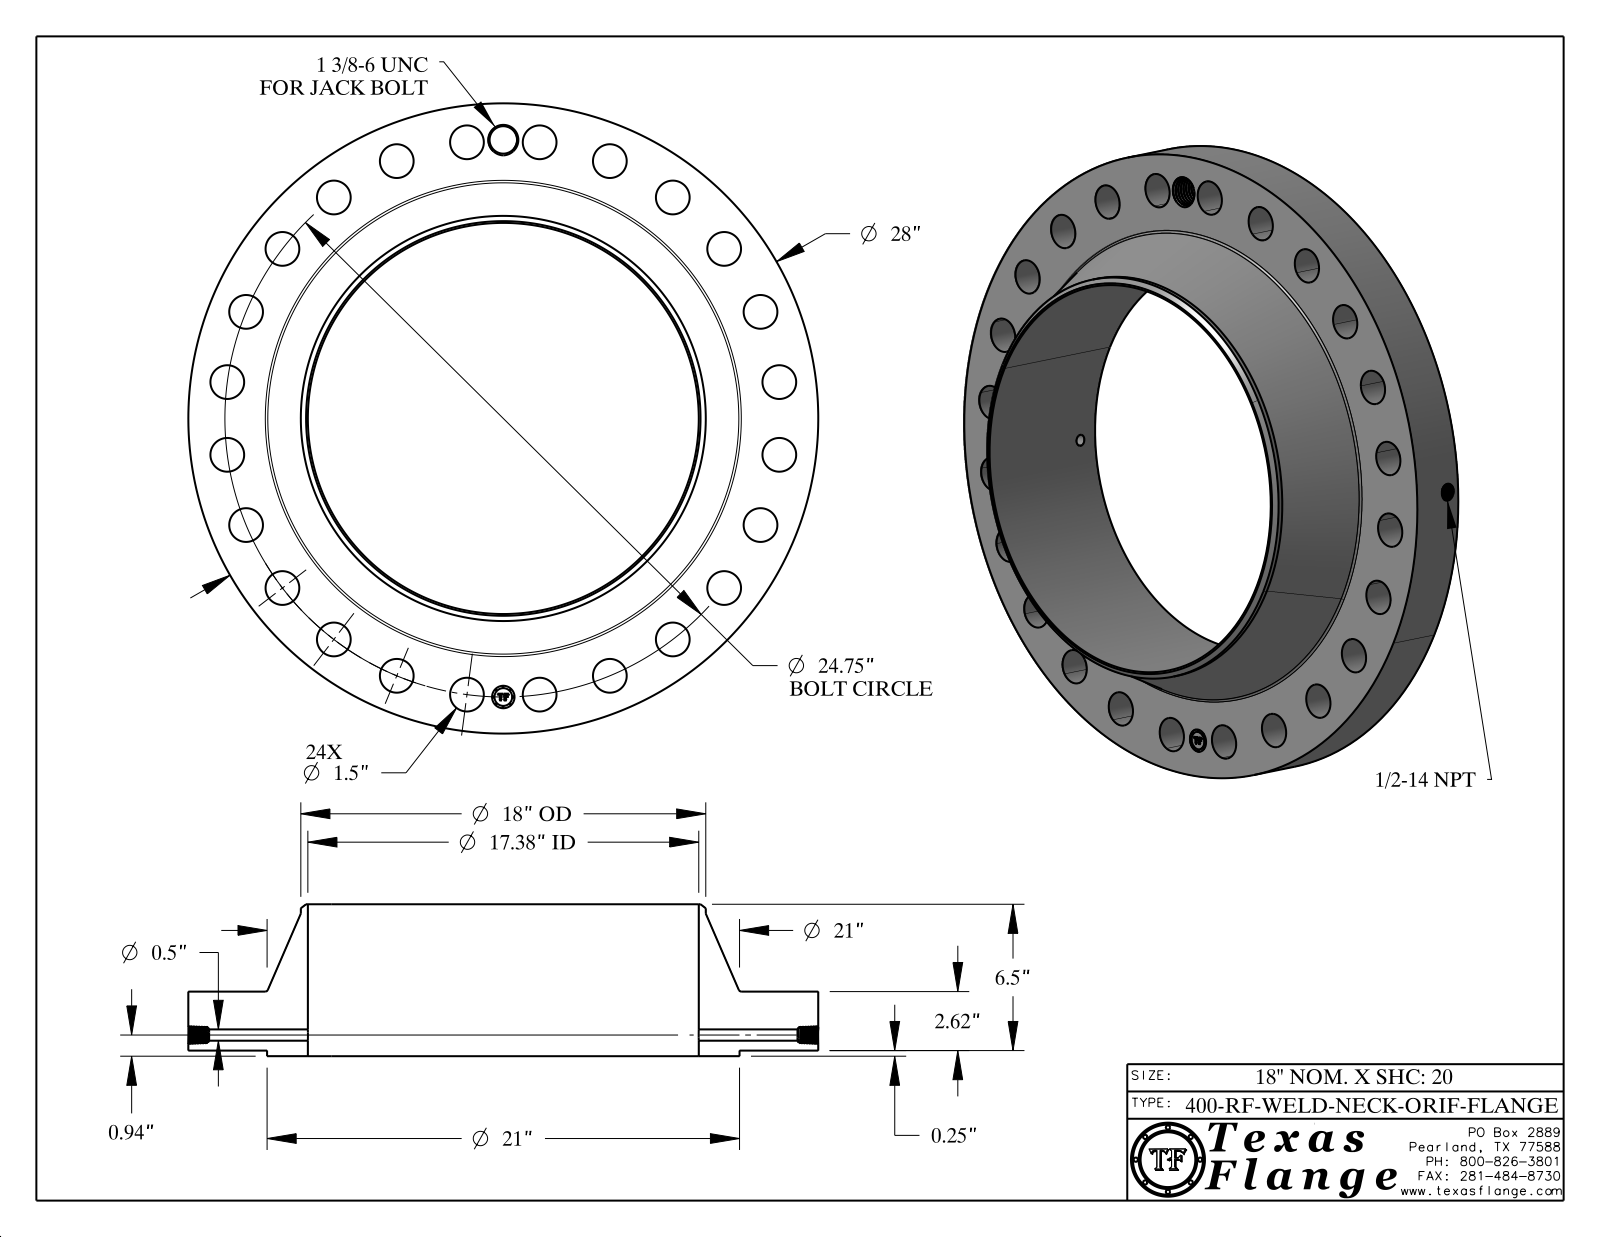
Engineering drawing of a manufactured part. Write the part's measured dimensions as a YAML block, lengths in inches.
part_name: "400-RF-WELD-NECK"
step_written_by: "CATIA V5 STEP AP214 (AUTOMOTIVE_DESIGN)"
units: inches
bodies: {solids: 1, faces: 806, planar: 369, cylindrical: 127, other: 310}
overall_size: [28, 28, 6.75]
volume: 1123
surface_area: 1771
round_holes:
  - {diameter: 1.5, count: 24}
  - {diameter: 0.5, count: 1}
  - {diameter: 0.672, count: 1}
  - {diameter: 1, count: 1}
  - {diameter: 1.219, count: 1}
  - {diameter: 17.376, count: 1}
round_bosses_or_shafts:
  - {diameter: 0.061, count: 8}
  - {diameter: 28, count: 1}
  - {diameter: 21, count: 1}
  - {diameter: 18, count: 1}
  - {diameter: 0.788, count: 1}
face_to_face_distances: [2.62, 0.25, 2.87, 6.75, 6.5, 3.88, 0.015, 2.855, 2.605, 3.895]
hole_center_spacings: [12.375, 15.067, 21.434, 22.866, 23.907, 6.406, 17.501, 3.23]
